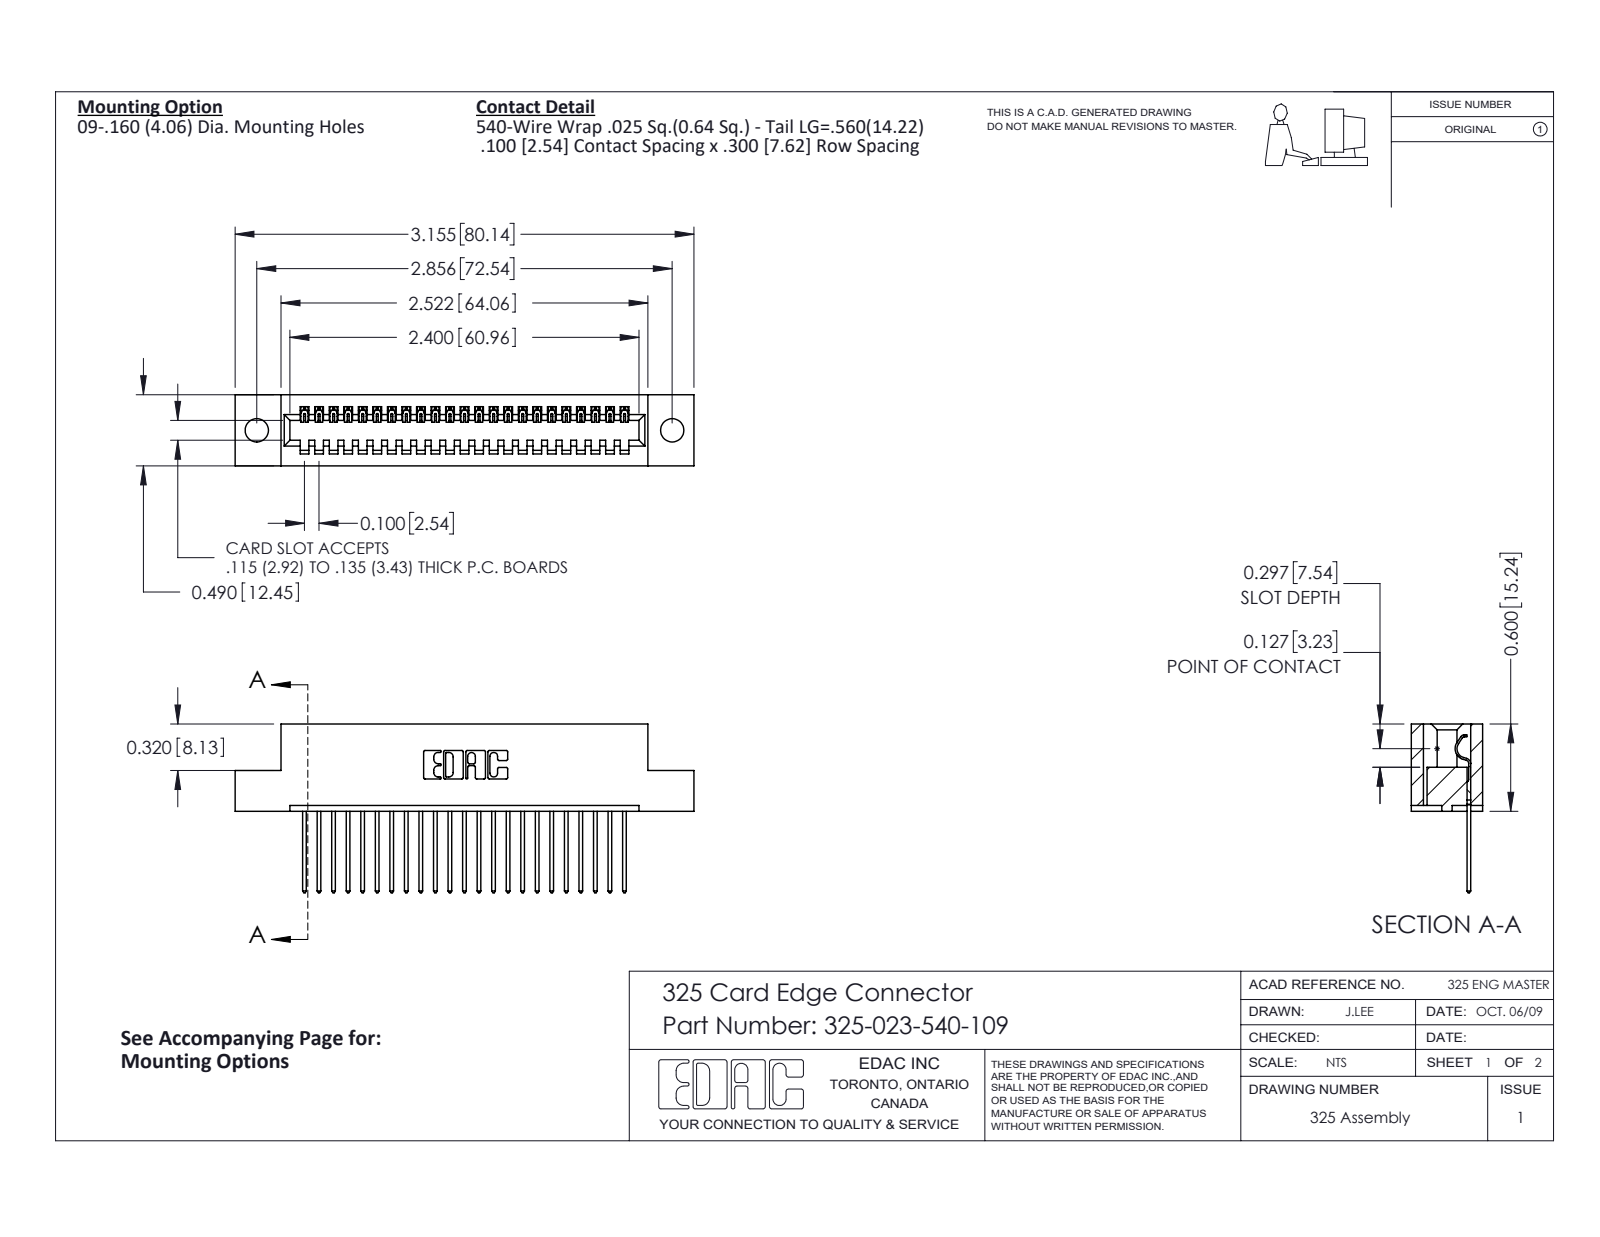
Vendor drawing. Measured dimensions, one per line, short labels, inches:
name: 325-292-001_325-293-140; 325-023-540-109; 325 Part_.160 TH
written by: SolidWorks 2016 (CONFIG_CONTROL_DESIGN)
unit: in
bodies: 24 solids, 1448 faces (1036 planar, 412 cylindrical, 0 other)
size: 3.155 × 1.16 × 0.49
volume: 0.6 in³; area: 16.33 in²
holes: 2× ⌀0.16
rounds: 46× R0.006, 46× R0.01, 22× R0.01, 6× R0.007, 6× R0.031, 3× R0.026, 1× R0.014, 1× R0.022
face distances: 0.083, 0.407, 0.3, 0.49, 0.107, 0.383, 0.025, 0.04, 0.325, 0.6
hole spacings: 2.856
